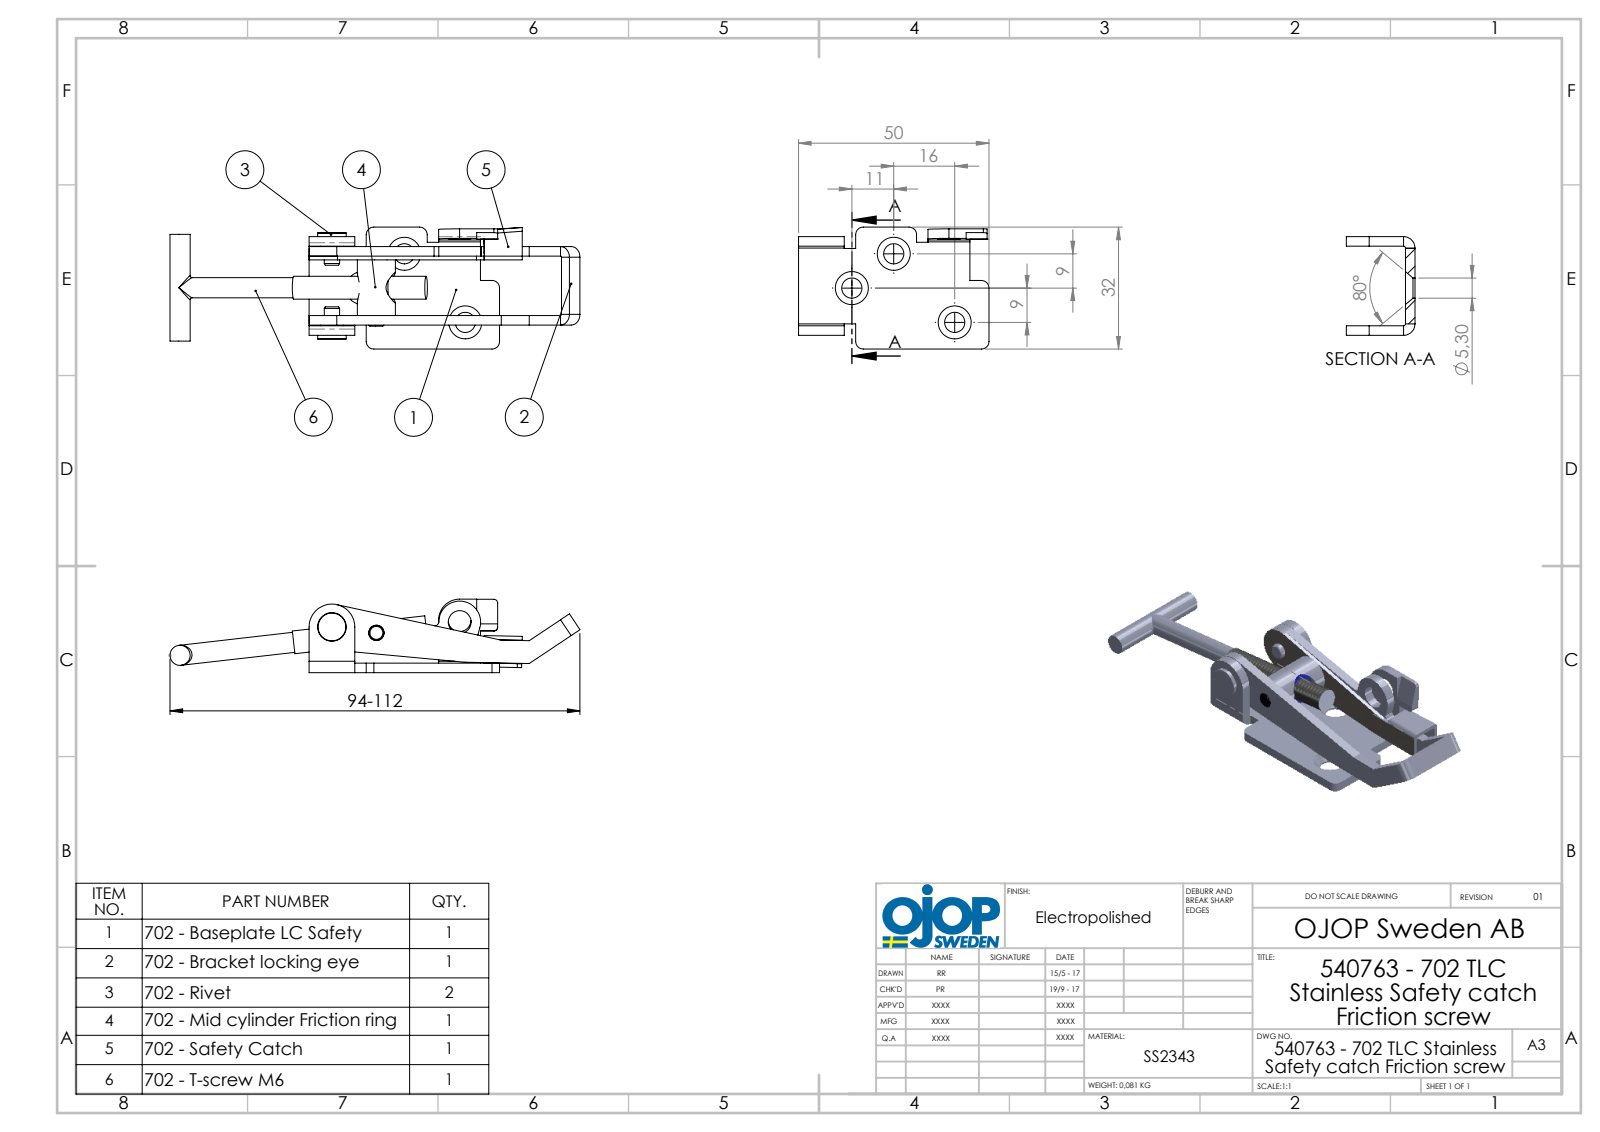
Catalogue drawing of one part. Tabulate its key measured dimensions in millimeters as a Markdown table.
| quantity | value |
| --- | --- |
| part name | 702 - Bygel låsögla; 702 - Friction Ring; 702 - T-skruv M6; 702 - Safety Catch (+5 more) |
| STEP written by | SolidWorks 2015 (AUTOMOTIVE_DESIGN) |
| units | millimeters |
| bodies | 8 solids, 215 faces (98 planar, 95 cylindrical, 22 other) |
| overall size | 107.61 × 32 × 19.3 |
| volume | 11 598 mm³ |
| surface area | 12 367 mm² |
| round holes (diameter × count) | 5.3 × 3, 6 × 3, 4 × 2, 4.1 × 2, 5 × 1, 5.1 × 1, 8 × 1 |
| round bosses / shafts (diameter × count) | 5.28 × 2, 10 × 1, 7.5 × 1, 6 × 1 |
| partial cylindrical surfaces (radius × count) | 1 × 11, 2 × 5, 0.5 × 3, 3 × 3, 0.3 × 2, 2.8 × 2, 5.5 × 2, 6 × 1 |
| main face-to-face distances | 2.5, 18.1, 1, 15.6, 3.5, 20.6, 14.6, 17.1, 23.4, 6.1 |
| hole center spacings | 11.77, 14.21, 22.04, 24.08, 28.46, 33.55 |
